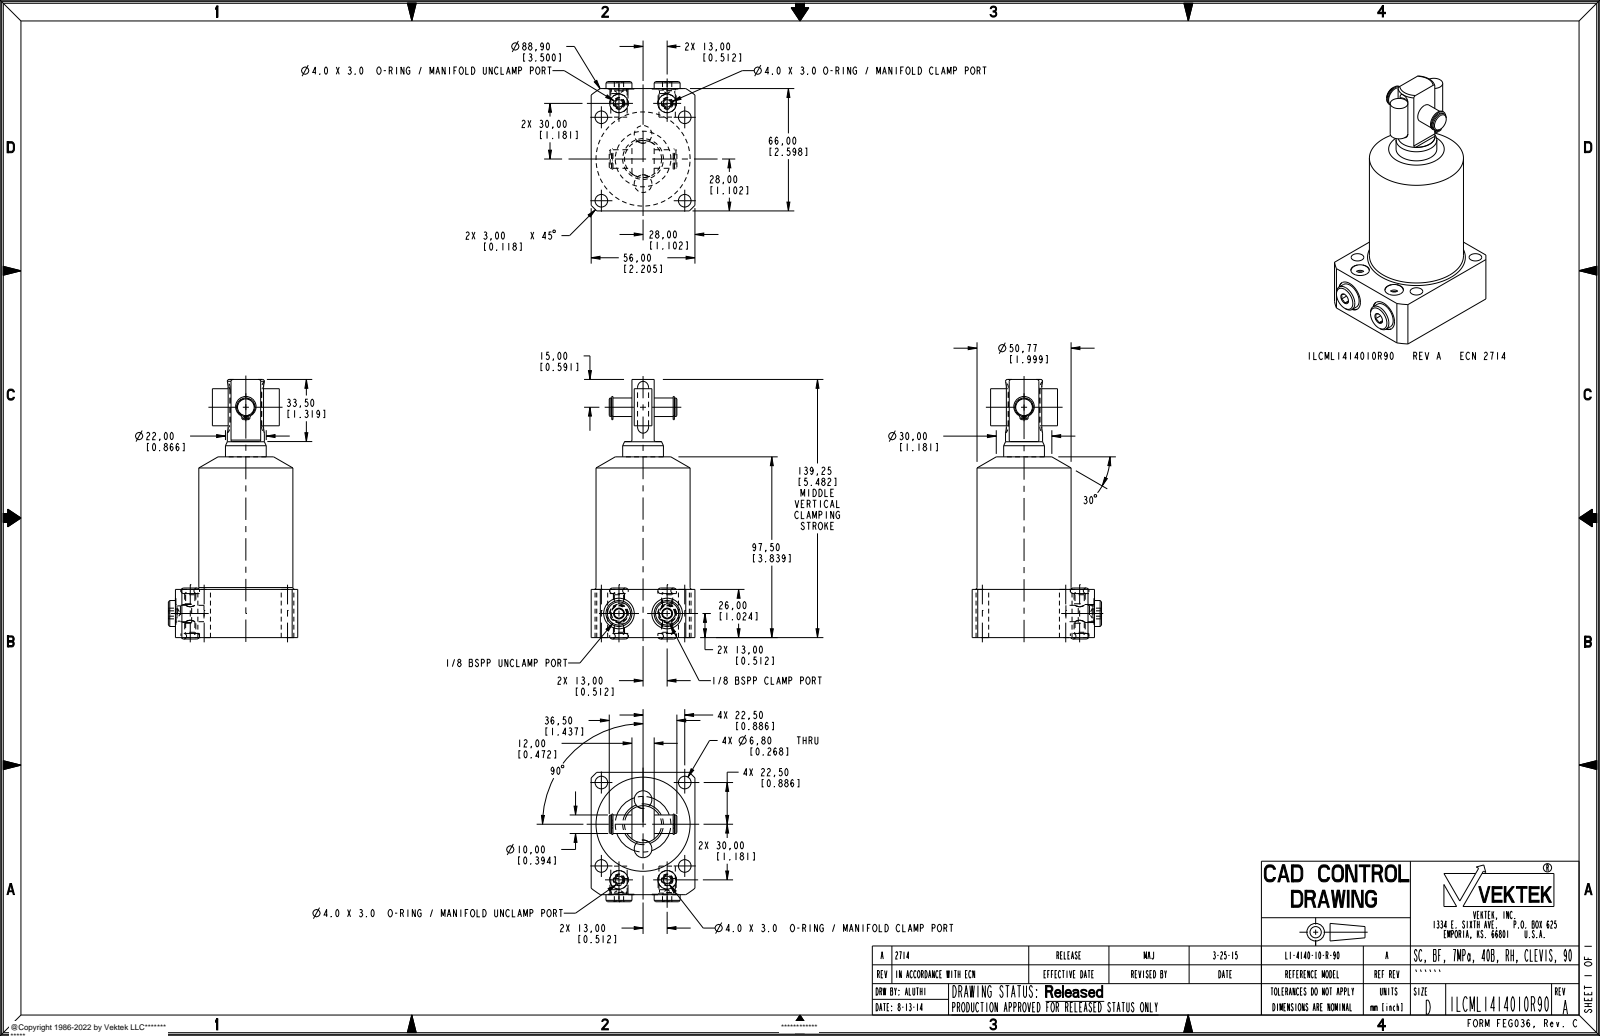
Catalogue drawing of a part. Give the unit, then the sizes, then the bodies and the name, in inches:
Units: inches
Overall size (bounding box): 5.512 × 2.748 × 2.205
Round holes (diameter × count): ⌀0.268 ×4, ⌀0.041 ×2, ⌀0.197 ×2, ⌀0.348 ×2, ⌀0.394 ×2, ⌀0.65 ×2
Round bosses / shafts (diameter × count): ⌀0.551 ×2, ⌀0.383 ×2, ⌀0.375 ×2, ⌀0.325 ×2, ⌀0.236 ×2, ⌀1.999 ×1, ⌀0.866 ×1, ⌀0.787 ×1
Partial cylindrical surfaces — rounded edges, fillets, slot ends (radius × count): R0.031 ×2, R0.041 ×2, R0.058 ×2, R0.187 ×2, R1.75 ×1
Main face-to-face distances: 2.205, 1.024, 0.866, 1.339, 2.598, 0.472, 3.839, 2.815, 0.197, 5.482
Hole centre spacings: 1.772, 0.476, 1.024, 1.428, 2.1, 2.495, 2.506, 0.092
Volume: 15 in³ · Surface area: 54.16 in²
Bodies: 7 solids, 234 faces (80 planar, 98 cylindrical, 56 other)
Part name (STEP PRODUCT): ILCML1414010R90
STEP written by: PRO/ENGINEER BY PARAMETRIC TECHNOLOGY CORPORATION, 2013320 (AUTOMOTIVE_DESIGN)
